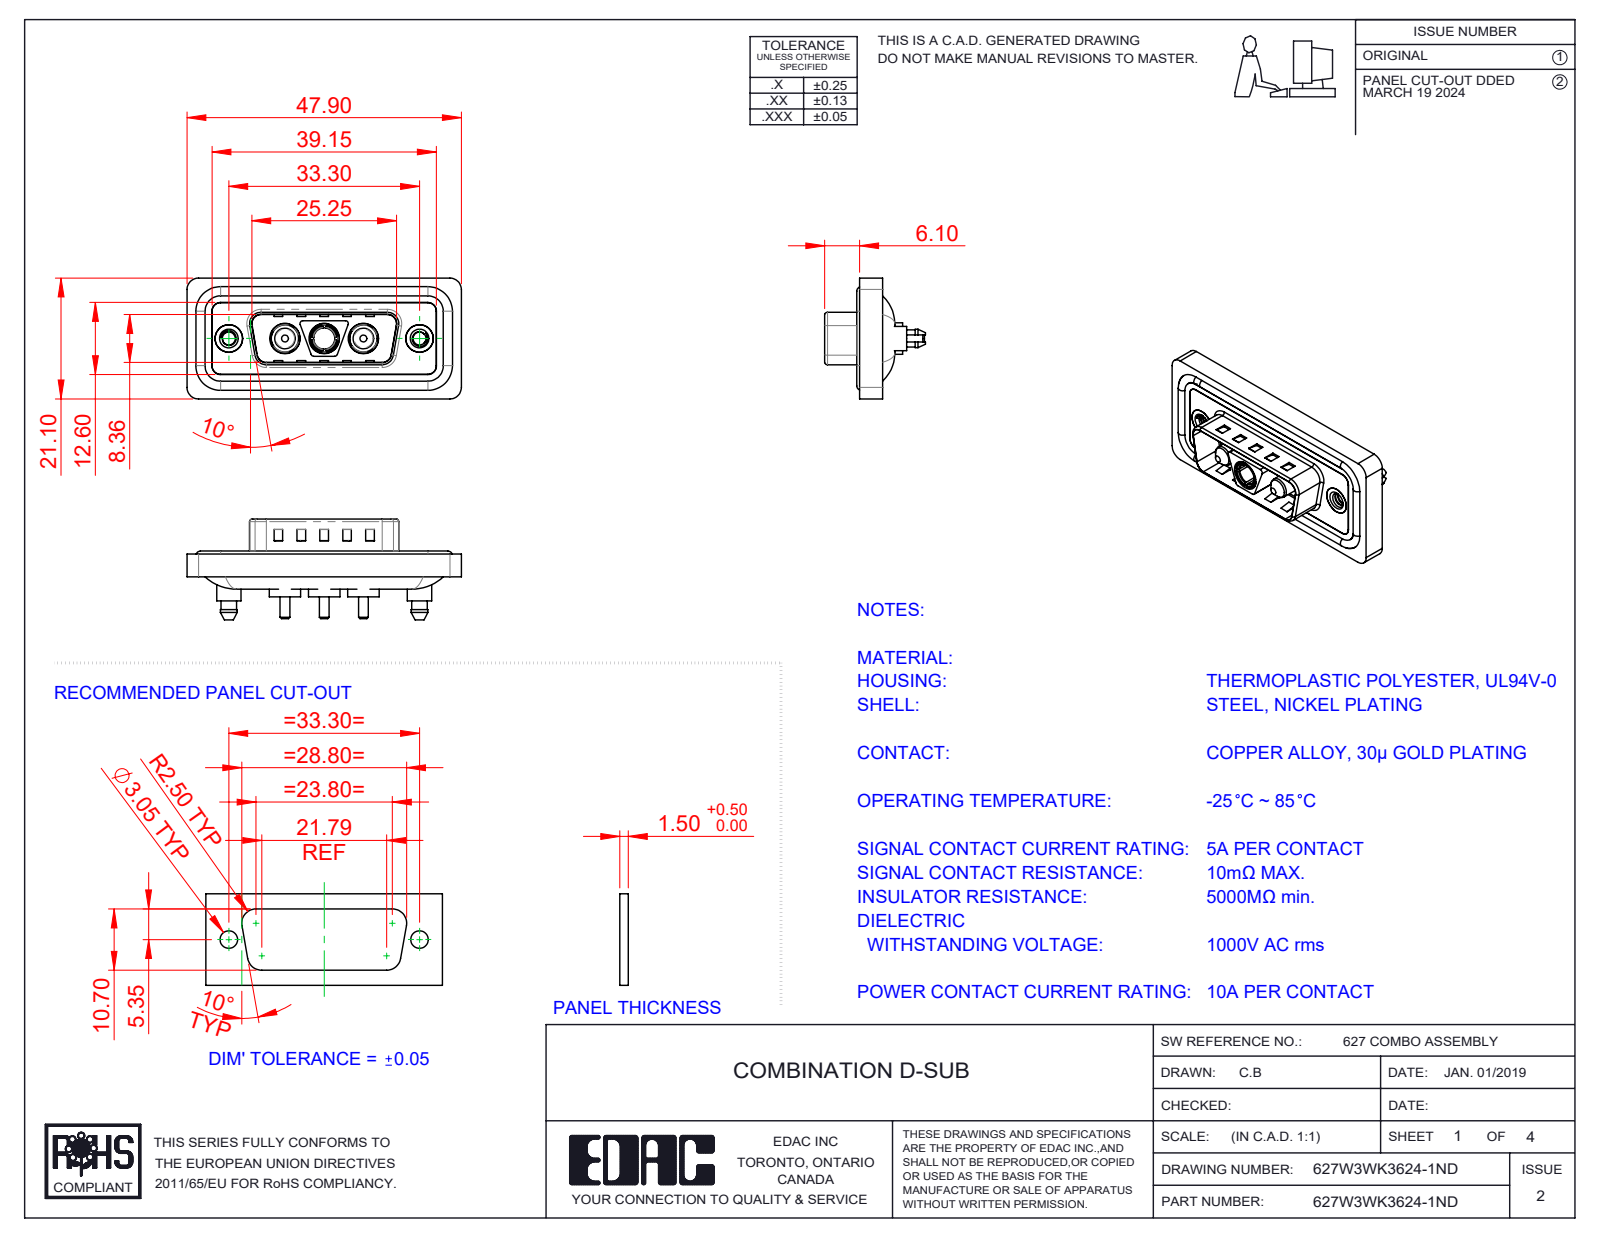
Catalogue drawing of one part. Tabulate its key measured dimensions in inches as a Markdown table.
| quantity | value |
| --- | --- |
| part name | 627Combo Waterproof Housing_15 Contacts; 627Combo Shell Front_15 Contacts; 627W3WK3624-1ND; Power Socket_10A S (+5 more) |
| STEP written by | SolidWorks 2023 (CONFIG_CONTROL_DESIGN) |
| units | inches |
| bodies | 13 solids, 667 faces (247 planar, 290 cylindrical, 130 other) |
| overall size | 1.886 × 0.831 × 0.693 |
| volume | 0.353 in³ |
| surface area | 14.61 in² |
| round holes (diameter × count) | 0.191 × 3, 0.209 × 3, 0.089 × 2, 0.157 × 2, 0.189 × 2, 0.197 × 2, 0.146 × 1 |
| round bosses / shafts (diameter × count) | 0.063 × 4, 0.217 × 3, 0.205 × 3, 0.187 × 3, 0.148 × 3, 0.067 × 3, 0.213 × 2, 0.193 × 2 |
| partial cylindrical surfaces (radius × count) | 0.059 × 28, 0.079 × 20, 0.02 × 12, 0.063 × 10, 0.01 × 4, 0.024 × 4, 0.026 × 4, 0.035 × 4 |
| main face-to-face distances | 0.016, 0.059, 0.043, 0.02, 0.063, 0.122, 0.114, 0.157, 0.028, 0.032 |
| hole center spacings | 0.27, 0.386, 0.656, 0.925, 0.539, 1.311 |
